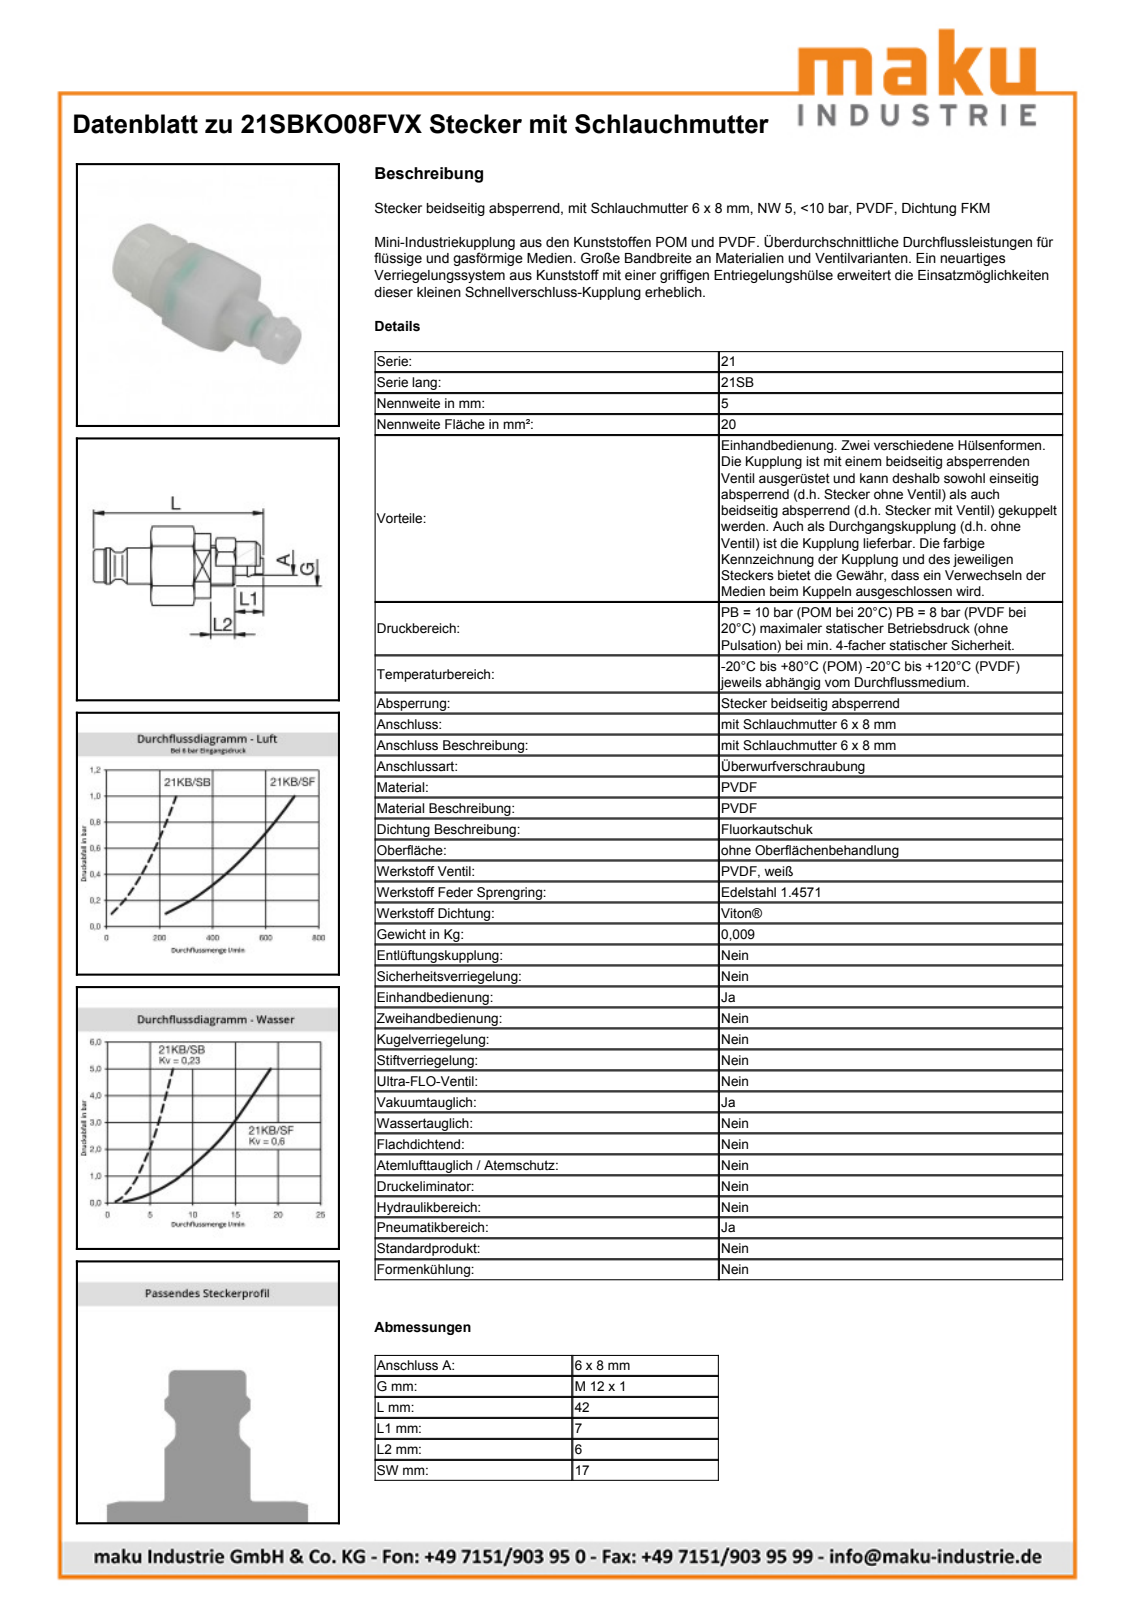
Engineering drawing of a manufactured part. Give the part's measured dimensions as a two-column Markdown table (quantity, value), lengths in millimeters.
| quantity | value |
| --- | --- |
| part name | D110750 |
| STEP written by | Autodesk Inventor 2013 (AUTOMOTIVE_DESIGN) |
| units | millimeters |
| bodies | 1 solid, 94 faces (28 planar, 35 cylindrical, 31 other) |
| overall size | 42.3 × 19.63 × 17 |
| volume | 5 671 mm³ |
| surface area | 3 195 mm² |
| round holes (diameter × count) | 6.2 × 1, 8.25 × 1, 10.92 × 1, 11.45 × 1, 13.3 × 1 |
| round bosses / shafts (diameter × count) | 12 × 1, 10.5 × 1, 9 × 1, 8.85 × 1, 8.55 × 1, 8.15 × 1, 6.7 × 1, 6.65 × 1 |
| partial cylindrical surfaces (radius × count) | 5 × 18, 8 × 1 |
| main face-to-face distances | 17, 14, 10.85, 4, 14.85, 21.05, 10.2, 6.2, 27.05, 16.2 |
